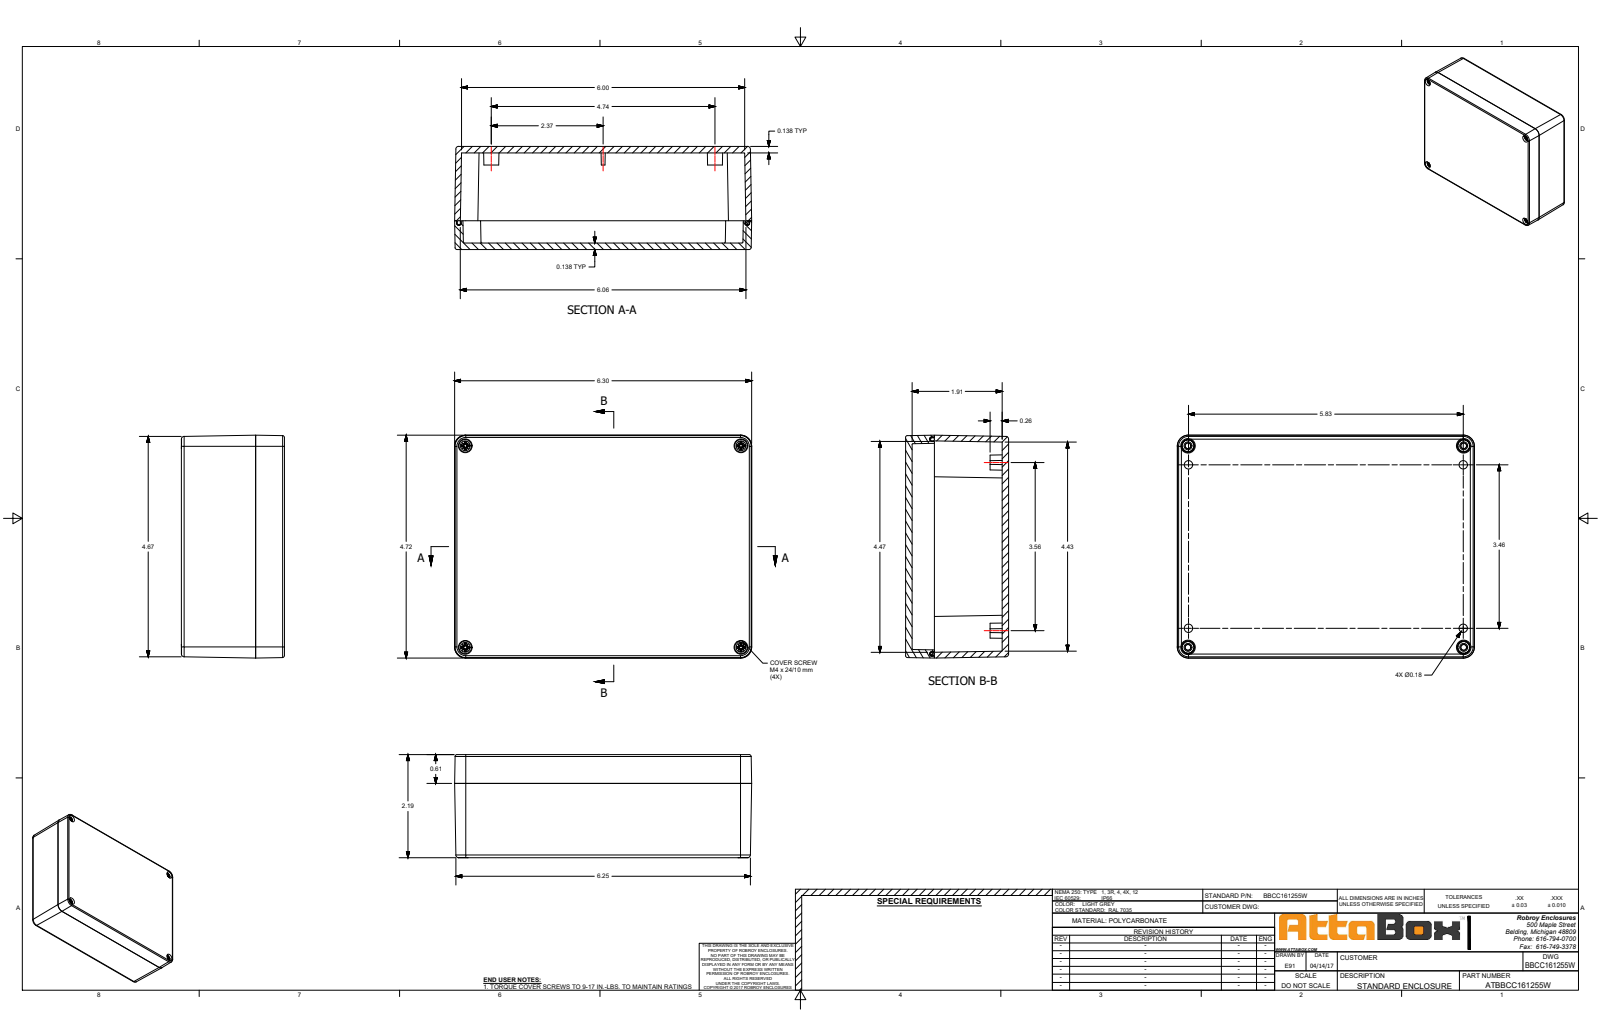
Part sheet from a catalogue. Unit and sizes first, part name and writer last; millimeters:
Units: millimetres
Overall size (bounding box): 160 × 120 × 55.5
Round holes (diameter × count): ⌀4.5 ×8, ⌀3.3 ×4, ⌀4.8 ×4, ⌀5.1 ×4, ⌀7 ×4, ⌀7.4 ×4, ⌀7.8 ×4
Round bosses / shafts (diameter × count): ⌀6.8 ×4, ⌀4.4 ×4, ⌀4 ×4, ⌀3.3 ×4
Partial cylindrical surfaces — rounded edges, fillets, slot ends (radius × count): R1 ×40, R0.5 ×30, R2.5 ×8, R4.9 ×8, R1.5 ×4, R2.6 ×4, R3.1 ×4, R3.6 ×4
Main face-to-face distances: 3.5, 52, 55.5, 48.5, 3.1, 120, 116.9, 115.6, 156.9, 160
Hole centre spacings: 10.3, 98.2, 148.6, 177.9, 88, 108.5, 148, 148.5
Volume: 234 700 mm³ · Surface area: 155 000 mm²
Bodies: 11 solids, 1555 faces (585 planar, 396 cylindrical, 574 other)
Part name (STEP PRODUCT): BBCC161255W
STEP written by: SolidWorks 2018 (AUTOMOTIVE_DESIGN)
